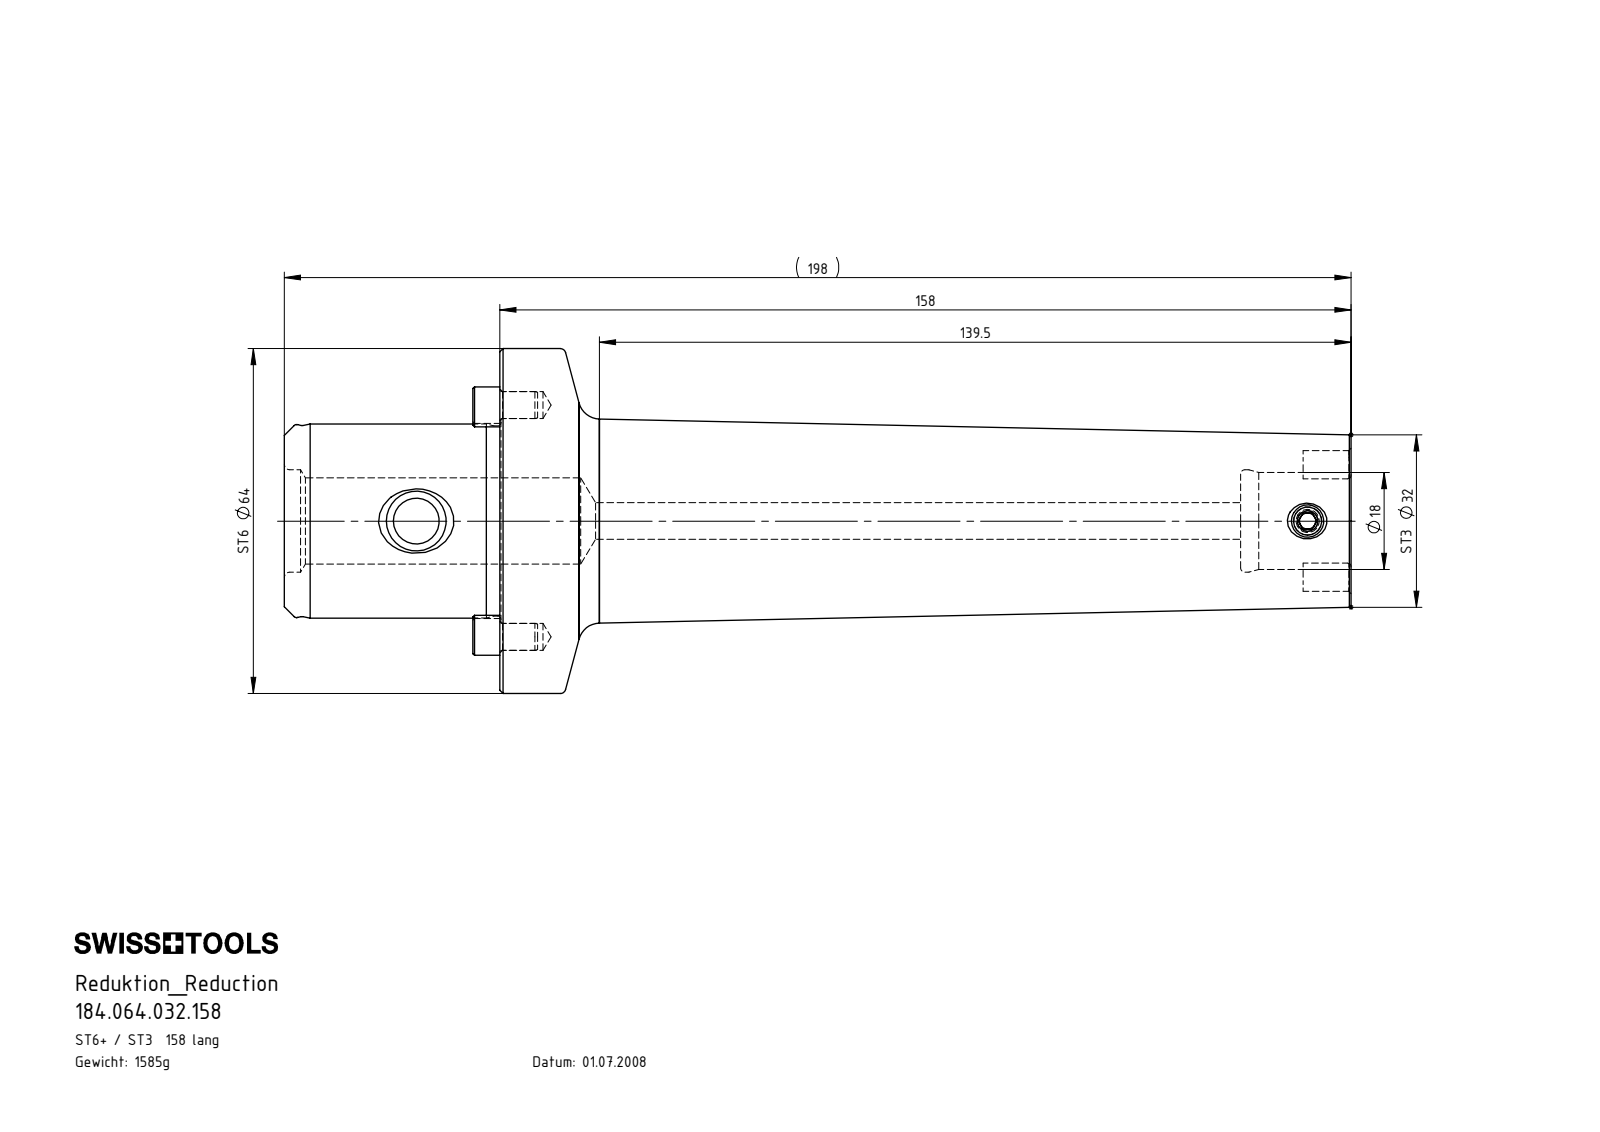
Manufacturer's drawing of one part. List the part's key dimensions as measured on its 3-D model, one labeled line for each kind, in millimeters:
Part name (STEP PRODUCT): ST6-ST3.K01.158_A; ST6-ER2.001.012_A; ST6-ST3.K01.158; ST3-ER1.001.008_A
STEP written by: SolidWorks 2015 (CONFIG_CONTROL_DESIGN)
Units: millimetres
Bodies: 4 solids, 166 faces (26 planar, 47 cylindrical, 93 other)
Overall size (bounding box): 198 × 64 × 64
Volume: 201 996 mm³ · Surface area: 36 411 mm²
Round holes (diameter × count): ⌀5 ×2, ⌀5.25 ×1, ⌀6.8 ×1, ⌀8.5 ×1, ⌀16 ×1, ⌀18 ×1, ⌀19 ×1
Round bosses / shafts (diameter × count): ⌀64 ×1, ⌀36 ×1, ⌀35.8 ×1, ⌀35.3 ×1, ⌀6 ×1
Partial cylindrical surfaces — rounded edges, fillets, slot ends (radius × count): R0.5 ×4, R2.5 ×2, R5.47 ×2, R18.05 ×2
Main face-to-face distances: 40, 198, 158, 177.5, 137.5, 20.5, 35, 5, 142.5, 163
Hole centre spacings: 21.5, 43, 165.45
